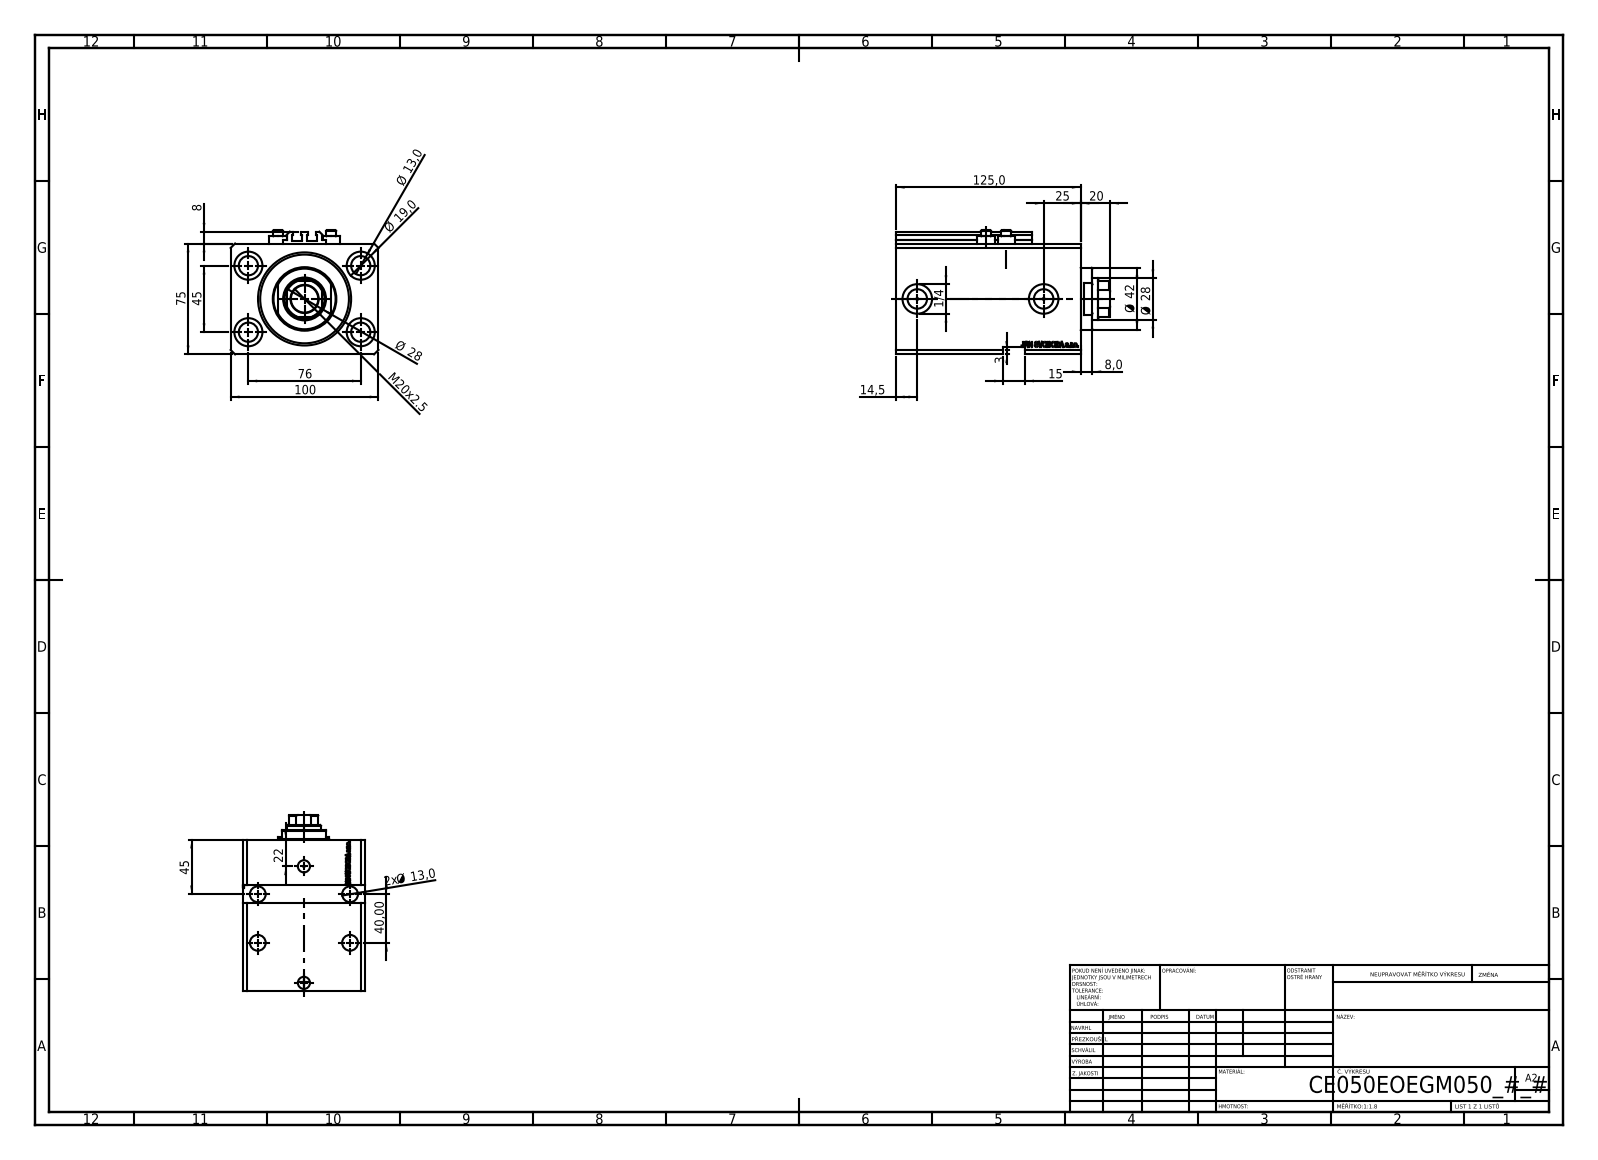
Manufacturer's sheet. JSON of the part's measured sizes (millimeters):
{"part_name": "V250CE_E_Body; V250CE_VC_E; ALLEN BOLT V250CE; V250CE_C_VCP", "step_written_by": "SolidWorks 2019 (CONFIG_CONTROL_DESIGN)", "units": "millimeters", "bodies": {"solids": 8, "faces": 1108, "planar": 535, "cylindrical": 146, "other": 427}, "overall_size": [145, 100, 84], "volume_mm3": 768812, "surface_area_mm2": 150350, "round_holes": [[13, 8], [1.25, 4], [4, 4], [19, 4], [10, 2], [13.16, 2], [20, 2], [18.5, 1], [28, 1], [50, 1], [63, 1]], "round_bosses_or_shafts": [[11.6, 4], [7, 4], [42, 1]], "partial_cylinders_radius": [[0.2, 10], [13.5, 1]], "face_to_face_distances": [75, 100, 125, 20, 11.9, 113.1, 105, 93.1, 70, 5], "hole_center_spacings": [44.16, 76, 13.6, 20.72, 27.59, 29, 33.62, 36]}
